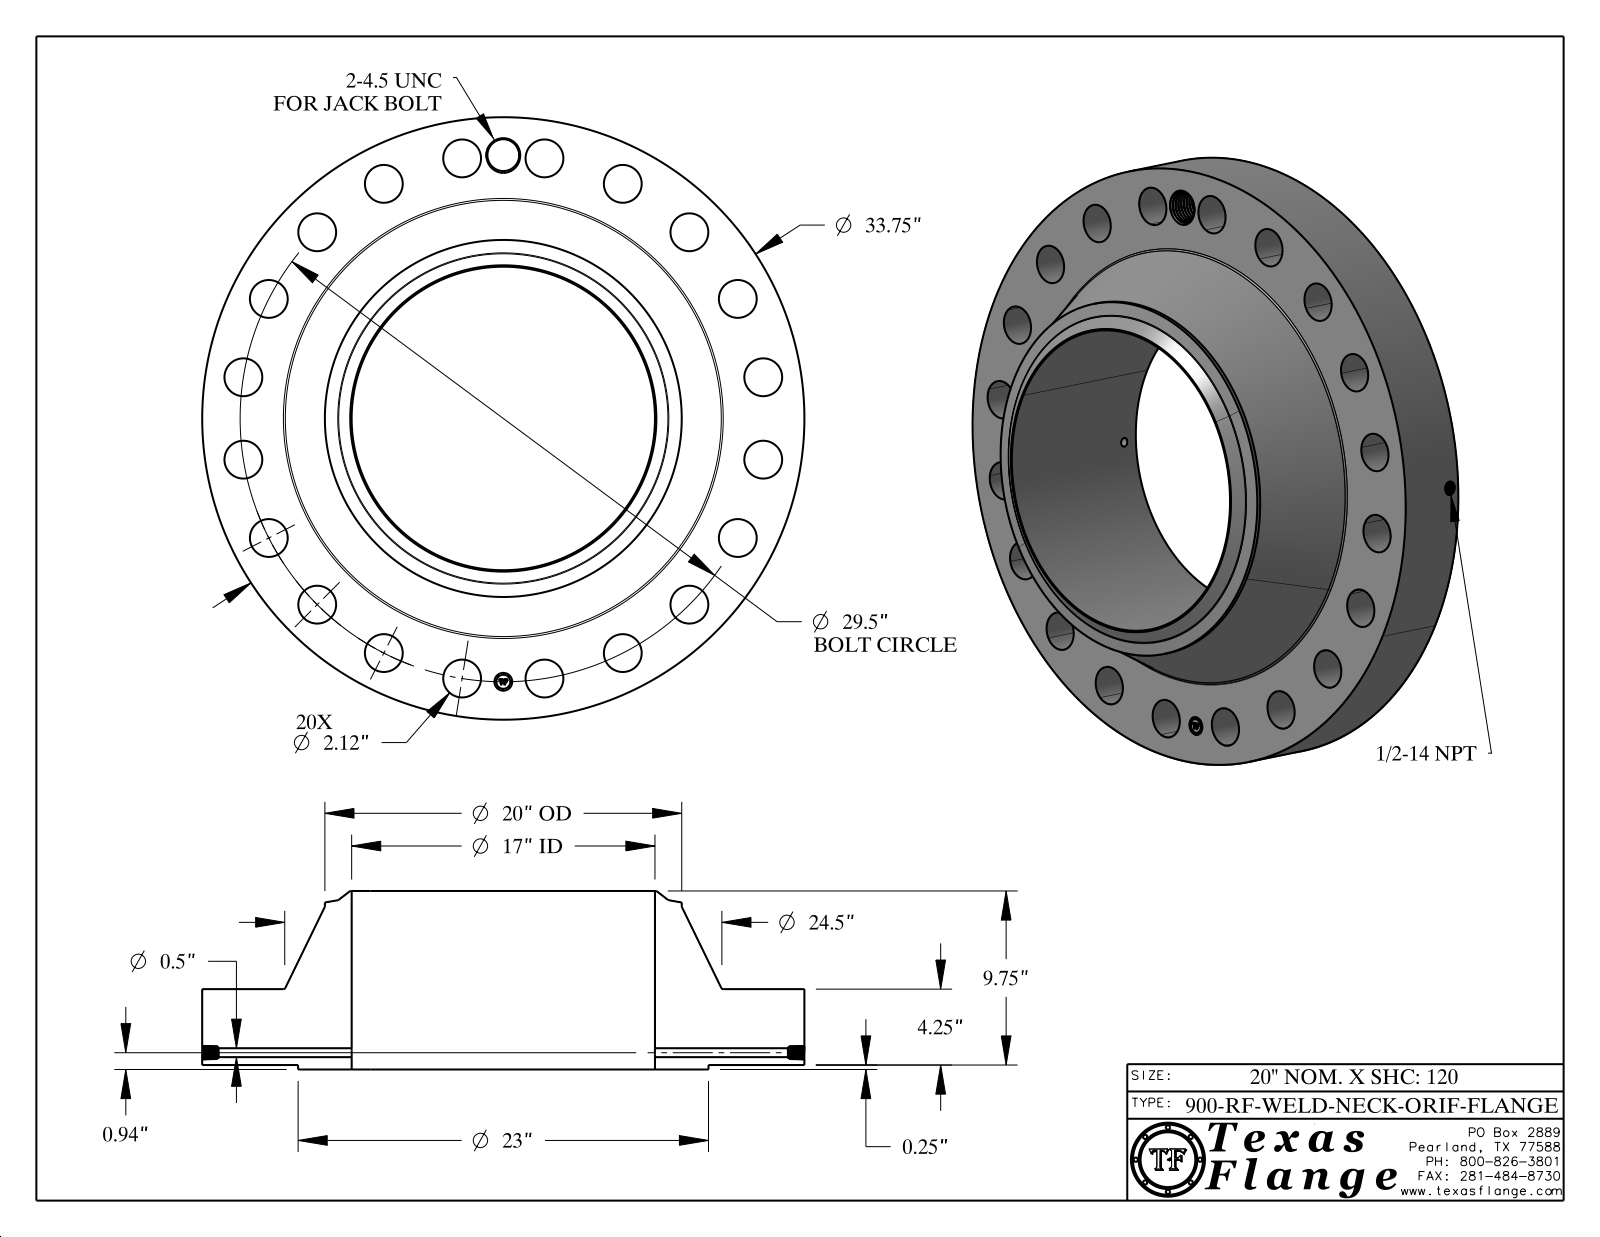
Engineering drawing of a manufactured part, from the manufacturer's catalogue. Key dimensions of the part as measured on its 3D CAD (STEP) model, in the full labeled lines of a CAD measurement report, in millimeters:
Part name (STEP PRODUCT): 900-RF-WELD-NECK
STEP written by: CATIA V5 STEP AP214 (AUTOMOTIVE_DESIGN)
Units: millimetres
Bodies: 1 solid, 822 faces (369 planar, 126 cylindrical, 327 other)
Overall size (bounding box): 857.3 × 857.3 × 254
Volume: 55 110 000 mm³ · Surface area: 1 966 000 mm²
Round holes (diameter × count): ⌀53.8 ×20, ⌀12.7 ×1, ⌀17.1 ×1, ⌀25.4 ×1, ⌀45.2 ×1, ⌀431.8 ×1
Round bosses / shafts (diameter × count): ⌀1.5 ×8, ⌀857.3 ×1, ⌀584.2 ×1, ⌀508 ×1, ⌀20 ×1
Main face-to-face distances: 108, 6.4, 114.3, 254, 247.7, 139.7, 113.9, 107.6, 0.4, 140.1
Hole centre spacings: 117.2, 231.5, 340.2, 440.4, 529.8, 606.2, 667.6, 740.1
